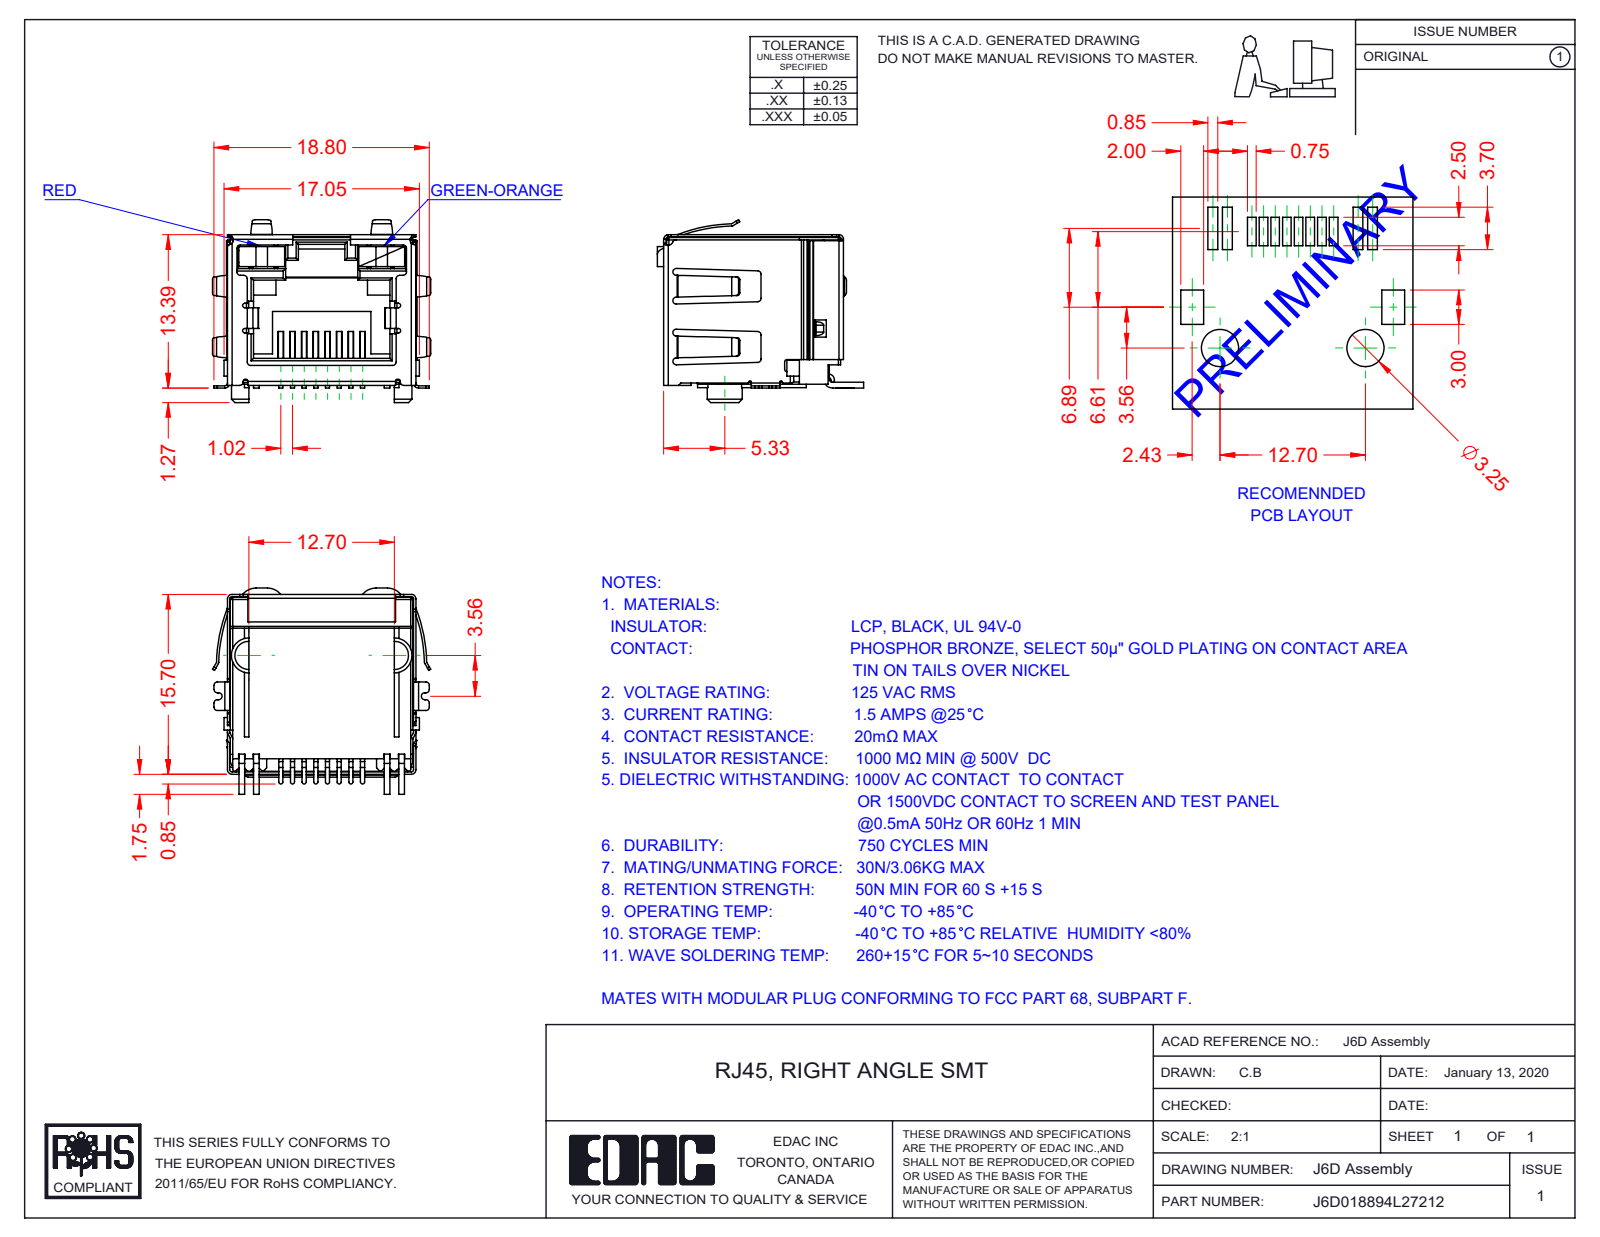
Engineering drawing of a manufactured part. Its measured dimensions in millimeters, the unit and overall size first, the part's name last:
Units: millimetres
Overall size (bounding box): 19.06 × 18 × 15.95
Partial cylindrical surfaces — rounded edges, fillets, slot ends (radius × count): R0.3 ×55, R0.2 ×40, R0.4 ×19, R0.25 ×16, R0.1 ×12, R0.15 ×8, R0.18 ×8, R0.5 ×6
Main face-to-face distances: 16, 16.2, 16.25, 2.25, 1, 15.95, 12.8, 0.45, 13.05, 10.6
Volume: 1 790 mm³ · Surface area: 4 796 mm²
Bodies: 12 solids, 1031 faces (702 planar, 284 cylindrical, 45 other)
Part name (STEP PRODUCT): 6D Insulator; J6D018894L27212; 6D Shield_LED - EMI; 6D LED RH_7-Green-Orange (+2 more)
STEP written by: SolidWorks 2016 (CONFIG_CONTROL_DESIGN)
